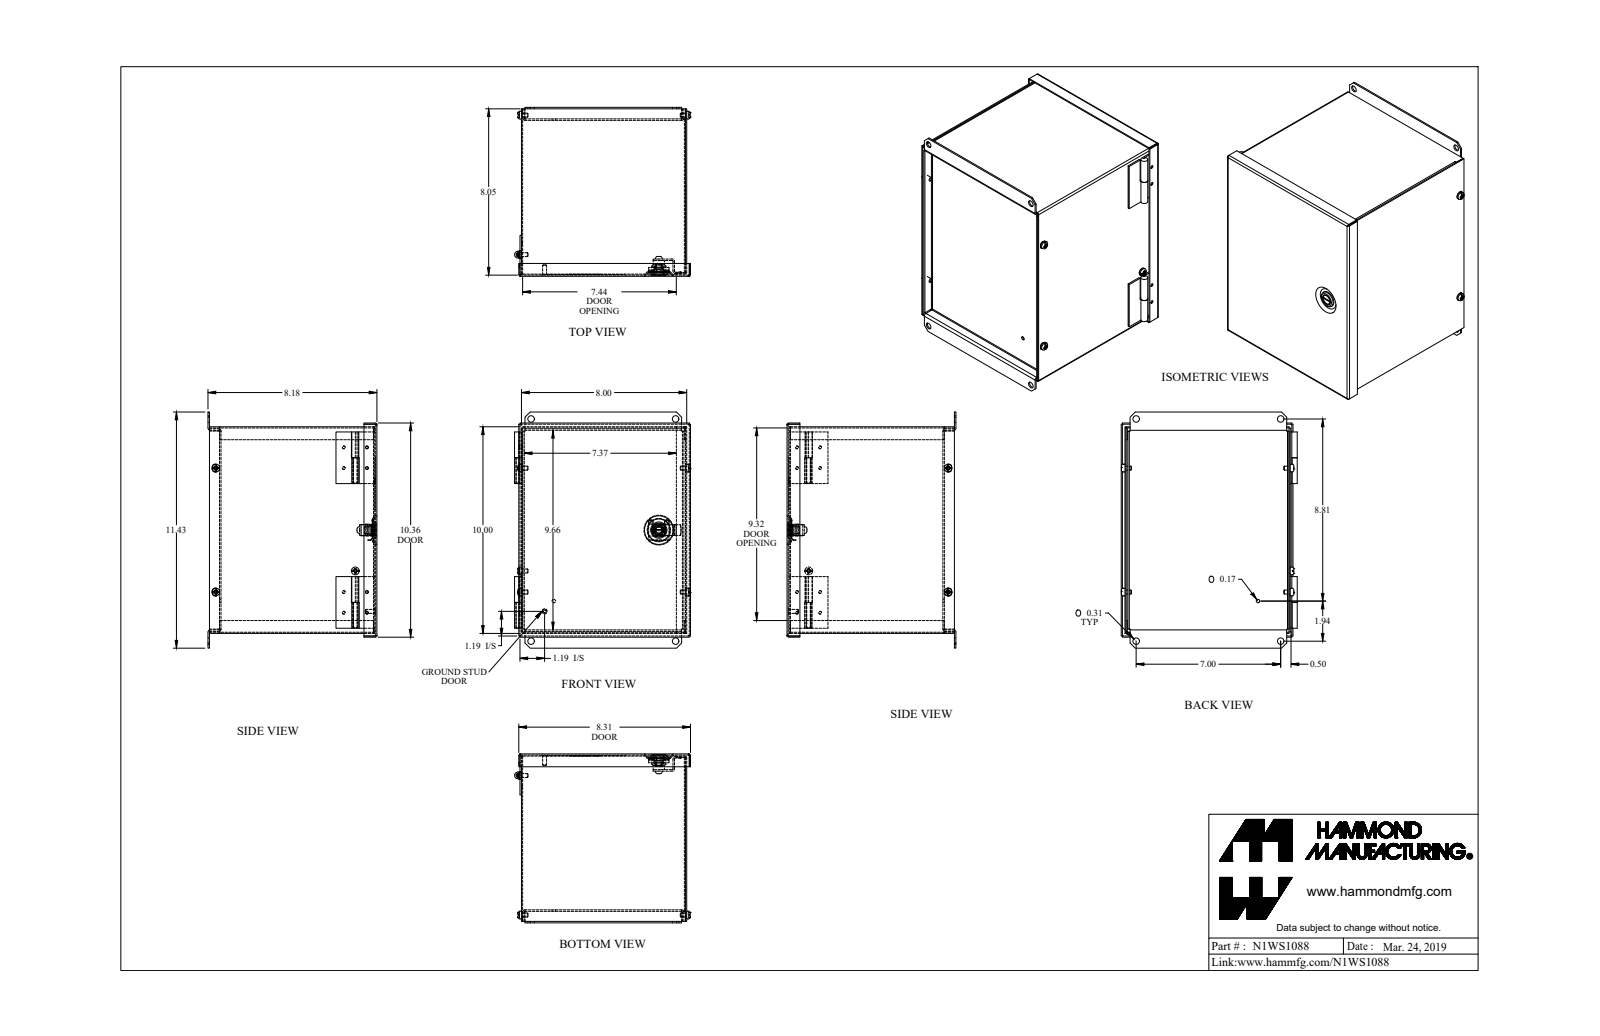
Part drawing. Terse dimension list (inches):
name: N1WS1088
written by: SolidWorks 2018 (AUTOMOTIVE_DESIGN)
unit: in
bodies: 15 solids, 539 faces (290 planar, 196 cylindrical, 53 other)
size: 11.425 × 8.519 × 8.179
volume: 31.99 in³; area: 1 066 in²
holes: 8× ⌀0.14, 4× ⌀0.17, 4× ⌀0.312, 1× ⌀0.187, 1× ⌀0.319, 1× ⌀0.476
bosses: 8× ⌀0.128, 3× ⌀0.375, 3× ⌀0.19, 1× ⌀0.787, 1× ⌀0.547, 1× ⌀0.472, 1× ⌀0.469, 1× ⌀0.366
rounds: 9× R0.029, 9× R0.086, 8× R0.036, 6× R0.108, 4× R0.012, 4× R0.1, 4× R0.109, 2× R0.079
face distances: 0.057, 7.943, 9.943, 0.072, 0.057, 8, 7.886, 7.621, 7.564, 7.492
hole spacings: 7, 1, 1.119, 1.501, 7.089, 6, 5.436, 6.104
